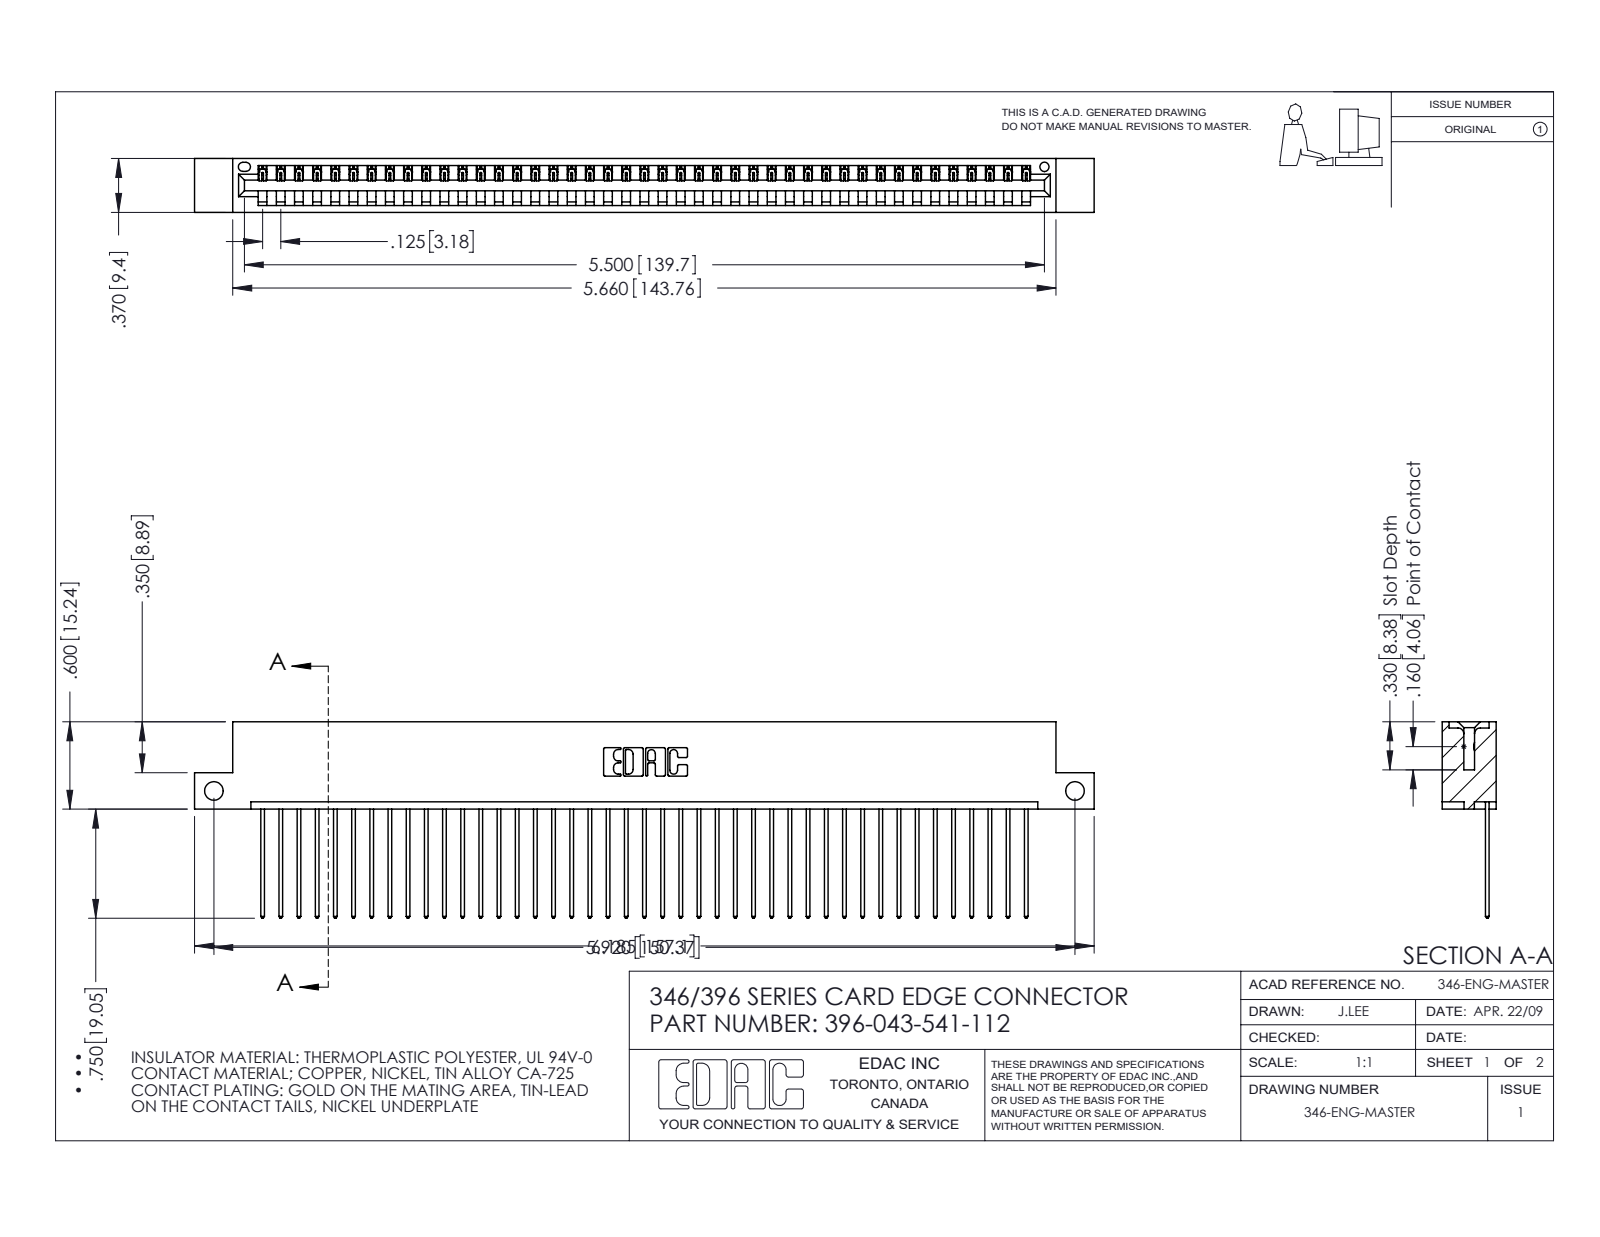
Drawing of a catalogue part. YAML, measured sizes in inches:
part_name: "396-043-541-112; 345-292-001_345-293-141; 346 Part_Flush Mounting Lugs - Side Mount"
step_written_by: "SolidWorks 2016 (CONFIG_CONTROL_DESIGN)"
units: inches
bodies: {solids: 44, faces: 2616, planar: 1796, cylindrical: 820, other: 0}
overall_size: [6.185, 1.35, 0.37]
volume: 0.921
surface_area: 30.36
round_holes:
  - {diameter: 0.128, count: 2}
  - {diameter: 0.064, count: 1}
partial_cylinders:
  - {radius: 0.006, count: 86}
  - {radius: 0.01, count: 86}
  - {radius: 0.01, count: 22}
  - {radius: 0.007, count: 6}
  - {radius: 0.031, count: 6}
  - {radius: 0.026, count: 3}
  - {radius: 0.031, count: 2}
  - {radius: 0.04, count: 2}
face_to_face_distances: [0.048, 0.322, 0.37, 0.25, 0.072, 0.298, 0.025, 0.148, 0.222, 0.1]
hole_center_spacings: [5.92]
